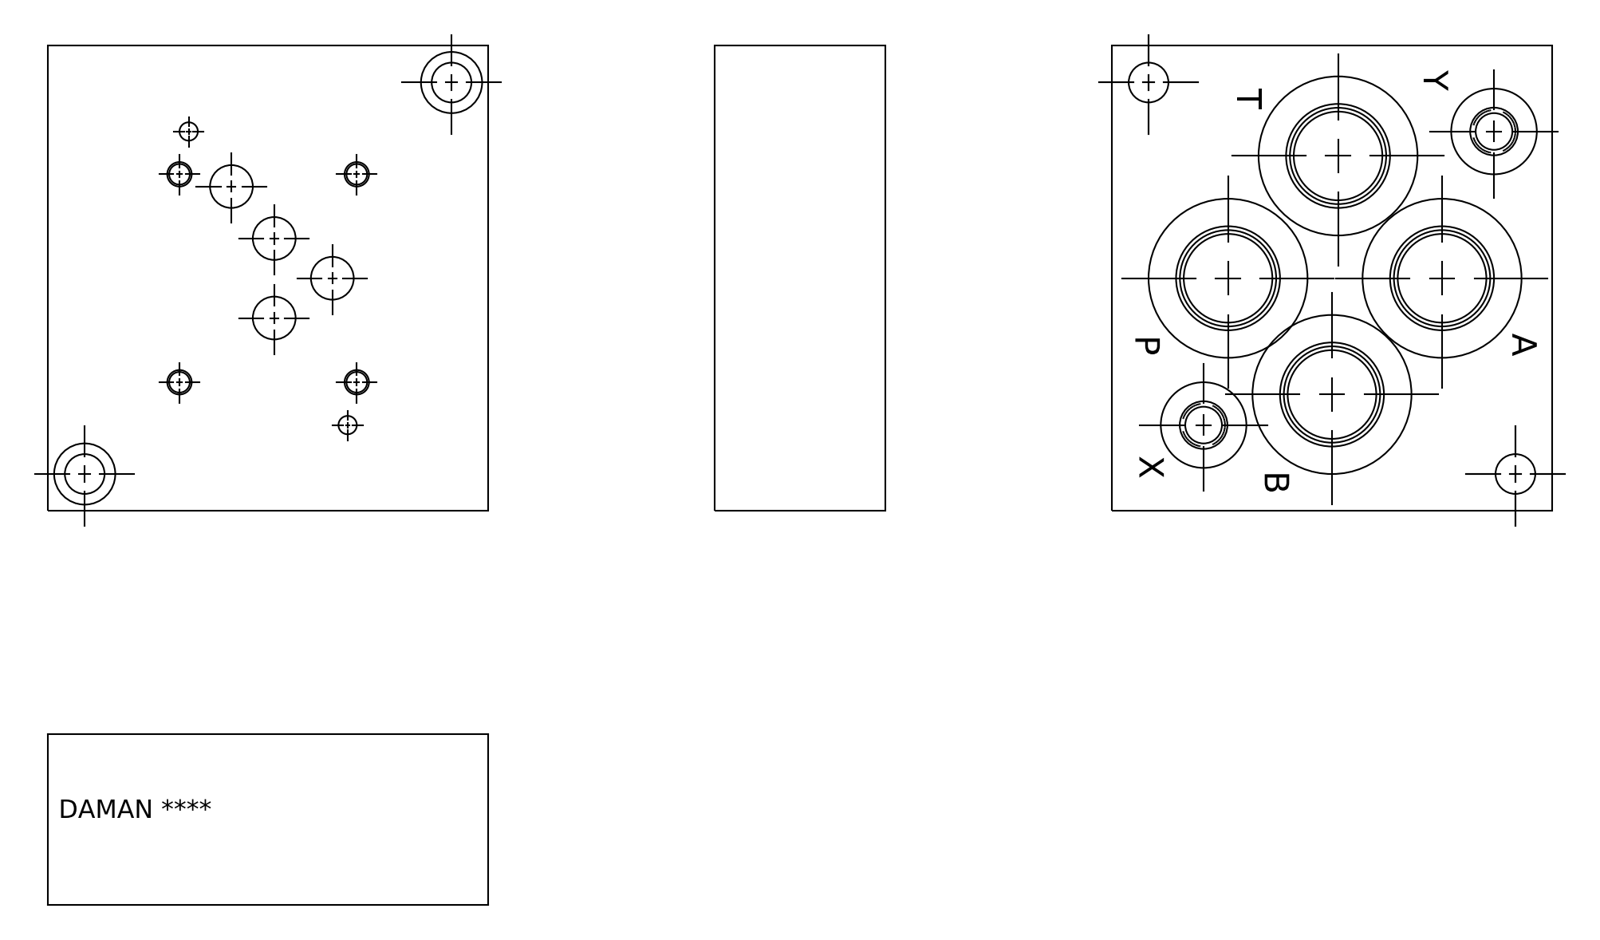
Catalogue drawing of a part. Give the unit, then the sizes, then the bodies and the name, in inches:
Units: inches
Overall size (bounding box): 4.75 × 4.5 × 1.75
Round holes (diameter × count): ⌀0.201 ×4, ⌀0.25 ×4, ⌀0.906 ×4, ⌀0.981 ×4, ⌀1.063 ×4, ⌀1.08 ×4, ⌀1.655 ×4, ⌀0.437 ×3, ⌀0.438 ×3, ⌀0.188 ×2, ⌀0.375 ×2, ⌀0.389 ×2
Main face-to-face distances: 1.75, 4.5, 4.75, 0.031, 1.719, 0.75, 0.969, 0.781, 1.188, 1.157
Hole centre spacings: 1.256, 1.774, 1.891, 2.293, 3.086, 0.404, 0.441, 0.447
Volume: 31.85 in³ · Surface area: 101 in²
Bodies: 1 solid, 536 faces (325 planar, 48 cylindrical, 163 other)
Part name (STEP PRODUCT): Part__D05HSPB12S_3D
STEP written by: Autodesk Inventor 2020 (AUTOMOTIVE_DESIGN)
